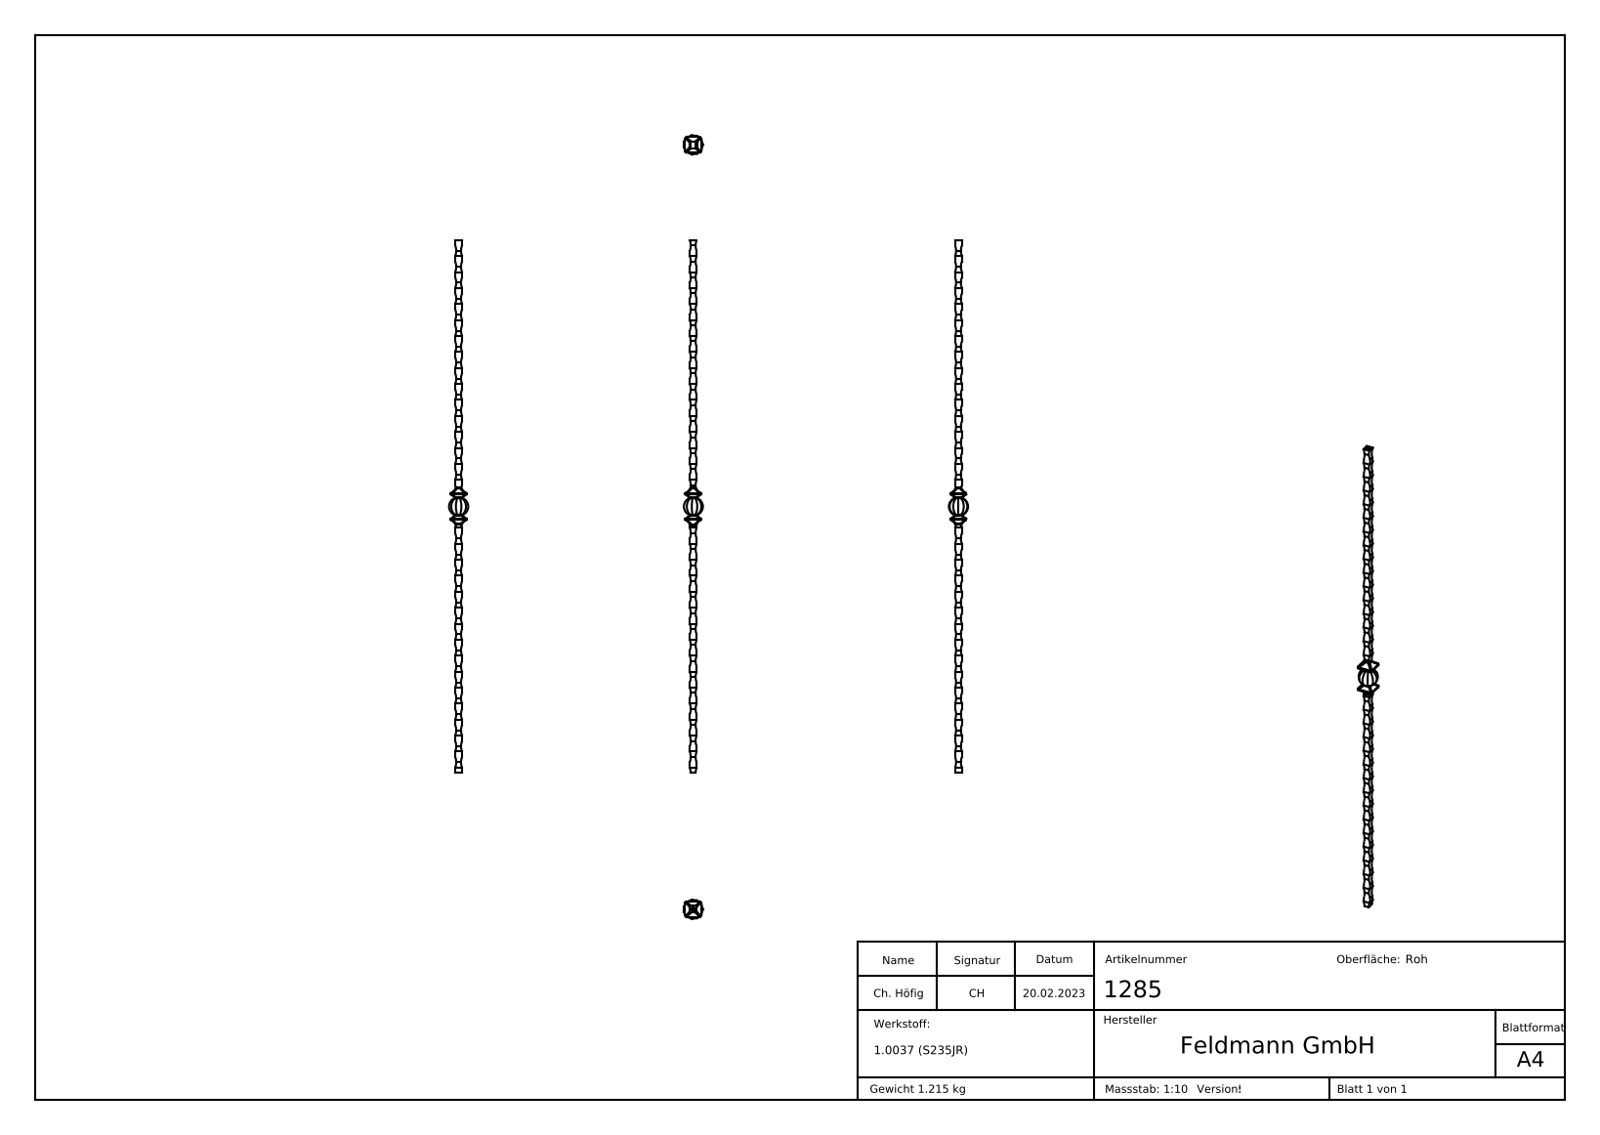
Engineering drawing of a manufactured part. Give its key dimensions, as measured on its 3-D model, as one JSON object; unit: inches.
{"part_name": "1285", "step_written_by": "SolidWorks 2018 (CONFIG_CONTROL_DESIGN)", "units": "inches", "bodies": {"solids": 1, "faces": 566, "planar": 264, "cylindrical": 163, "other": 139}, "overall_size": [39.37, 1.422, 1.407], "volume_in3": 9.508, "surface_area_in2": 78.71, "partial_cylinders_radius": [[1.024, 128], [0.118, 16], [0.689, 11]], "face_to_face_distances": [0.512, 0.74, 0.335, 0.846, 1.181, 39.37, 0.315, 0.866, 0.02, 0.531]}
